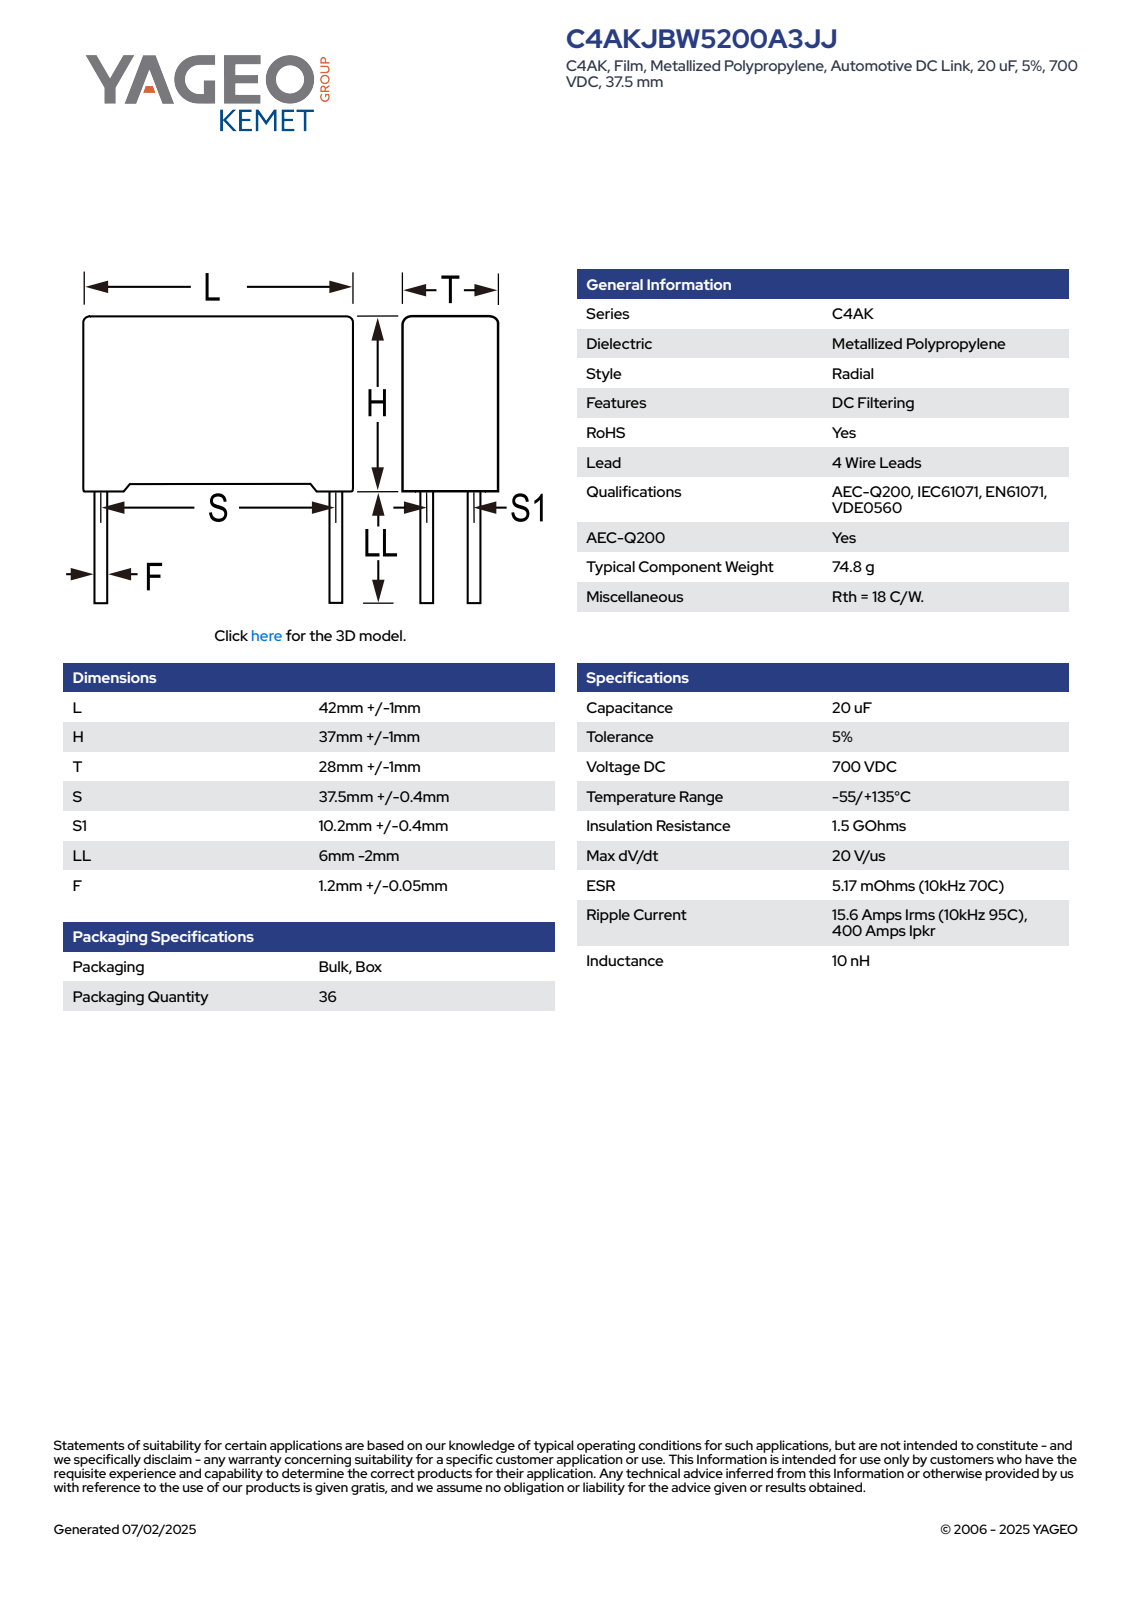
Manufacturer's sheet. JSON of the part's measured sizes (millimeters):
{"part_name": "CFP_RB4_42X37X28_L43H38T29S37.5S110.2LL4F1.25", "step_written_by": "SolidWorks 2014 (AUTOMOTIVE_DESIGN)", "units": "millimeters", "bodies": {"solids": 4, "faces": 87, "planar": 79, "cylindrical": 8, "other": 0}, "overall_size": [43, 42, 29], "volume_mm3": 46180, "surface_area_mm2": 8190, "round_bosses_or_shafts": [[1.25, 4]], "face_to_face_distances": [29, 43, 36.88, 1.12, 38, 1.78, 29.01, 41.22, 39.44, 27.22]}
